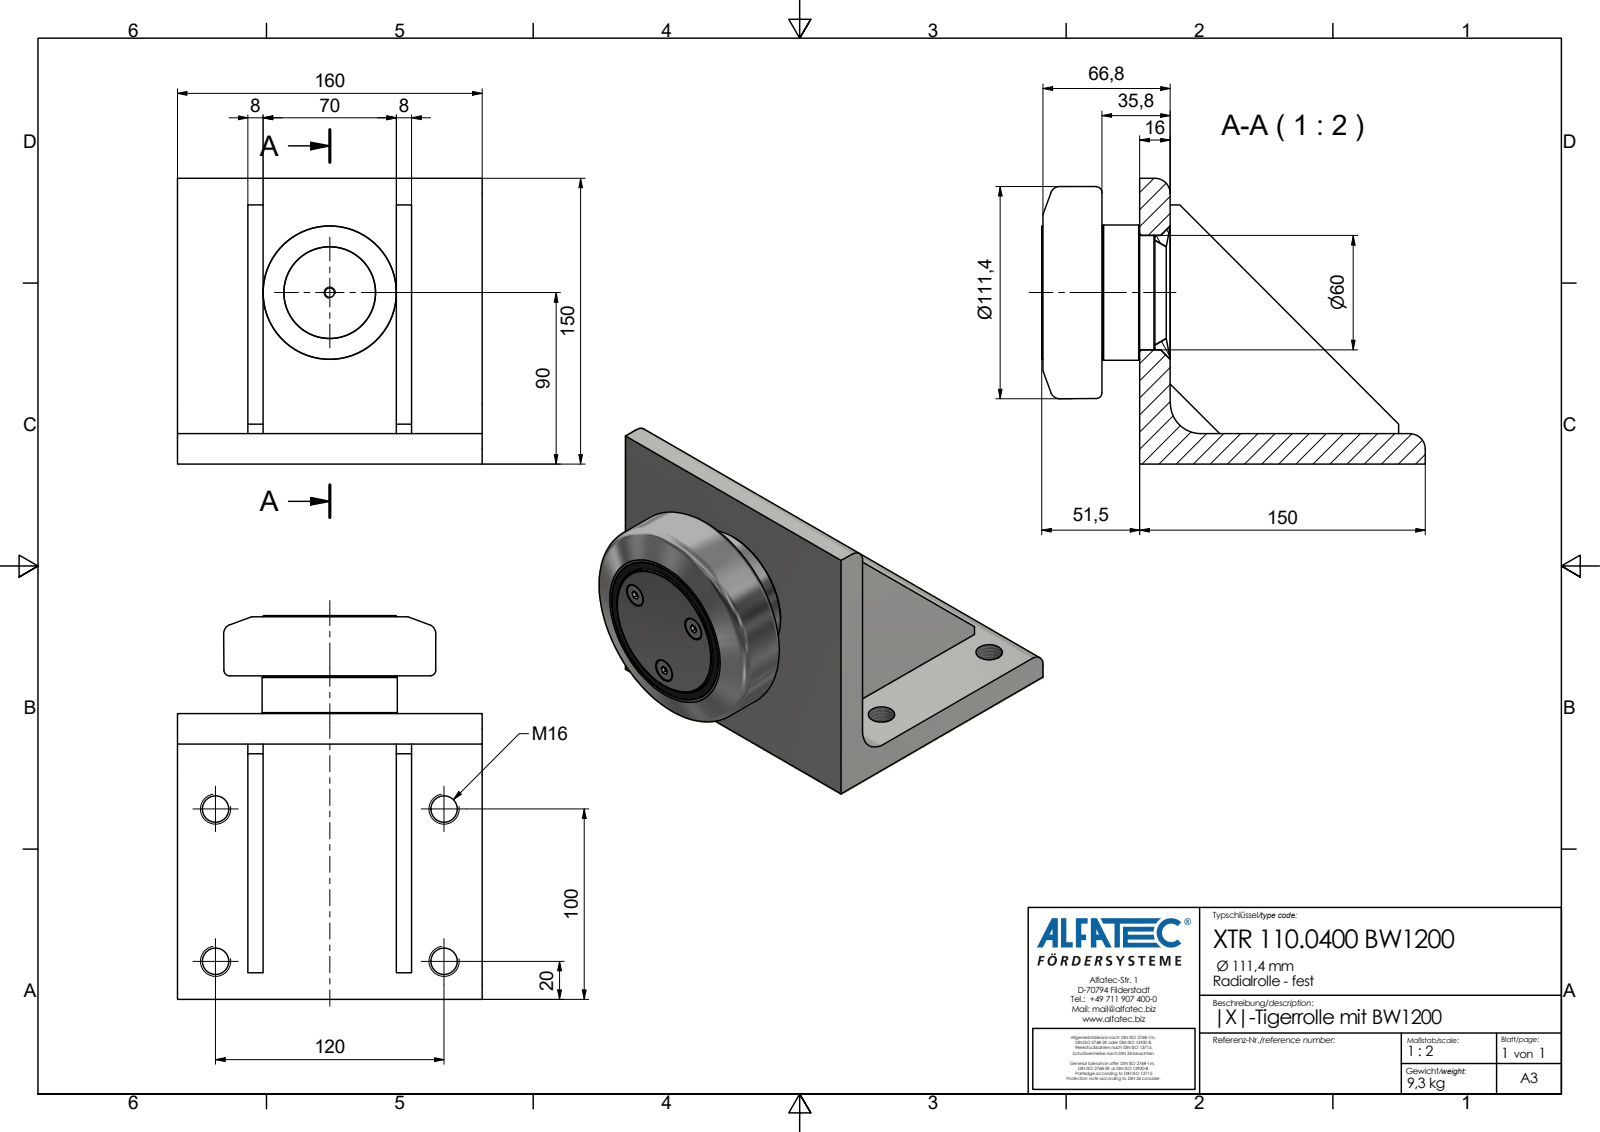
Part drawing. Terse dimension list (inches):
name: XTR 110.0400 BW1200_Kontur
written by: Autodesk Inventor 2020 (AP242_MANAGED_MODEL_BASED_3D_ENGINEERING_MIM_LF)
unit: in
bodies: 1 solid, 74 faces (51 planar, 16 cylindrical, 7 other)
size: 7.933 × 6.299 × 5.906
volume: 73.84 in³; area: 247.5 in²
holes: 4× ⌀0.545, 3× ⌀0.488
bosses: 3× ⌀0.461, 1× ⌀2.795, 1× ⌀2.776, 1× ⌀2.756
rounds: 2× R0.315, 1× R0.63
face distances: 0.63, 0.315, 3.071, 1.457, 1.772, 4.528, 4.843, 3.386, 2.756, 0.78
hole spacings: 1.705, 3.15, 4.724, 5.678
